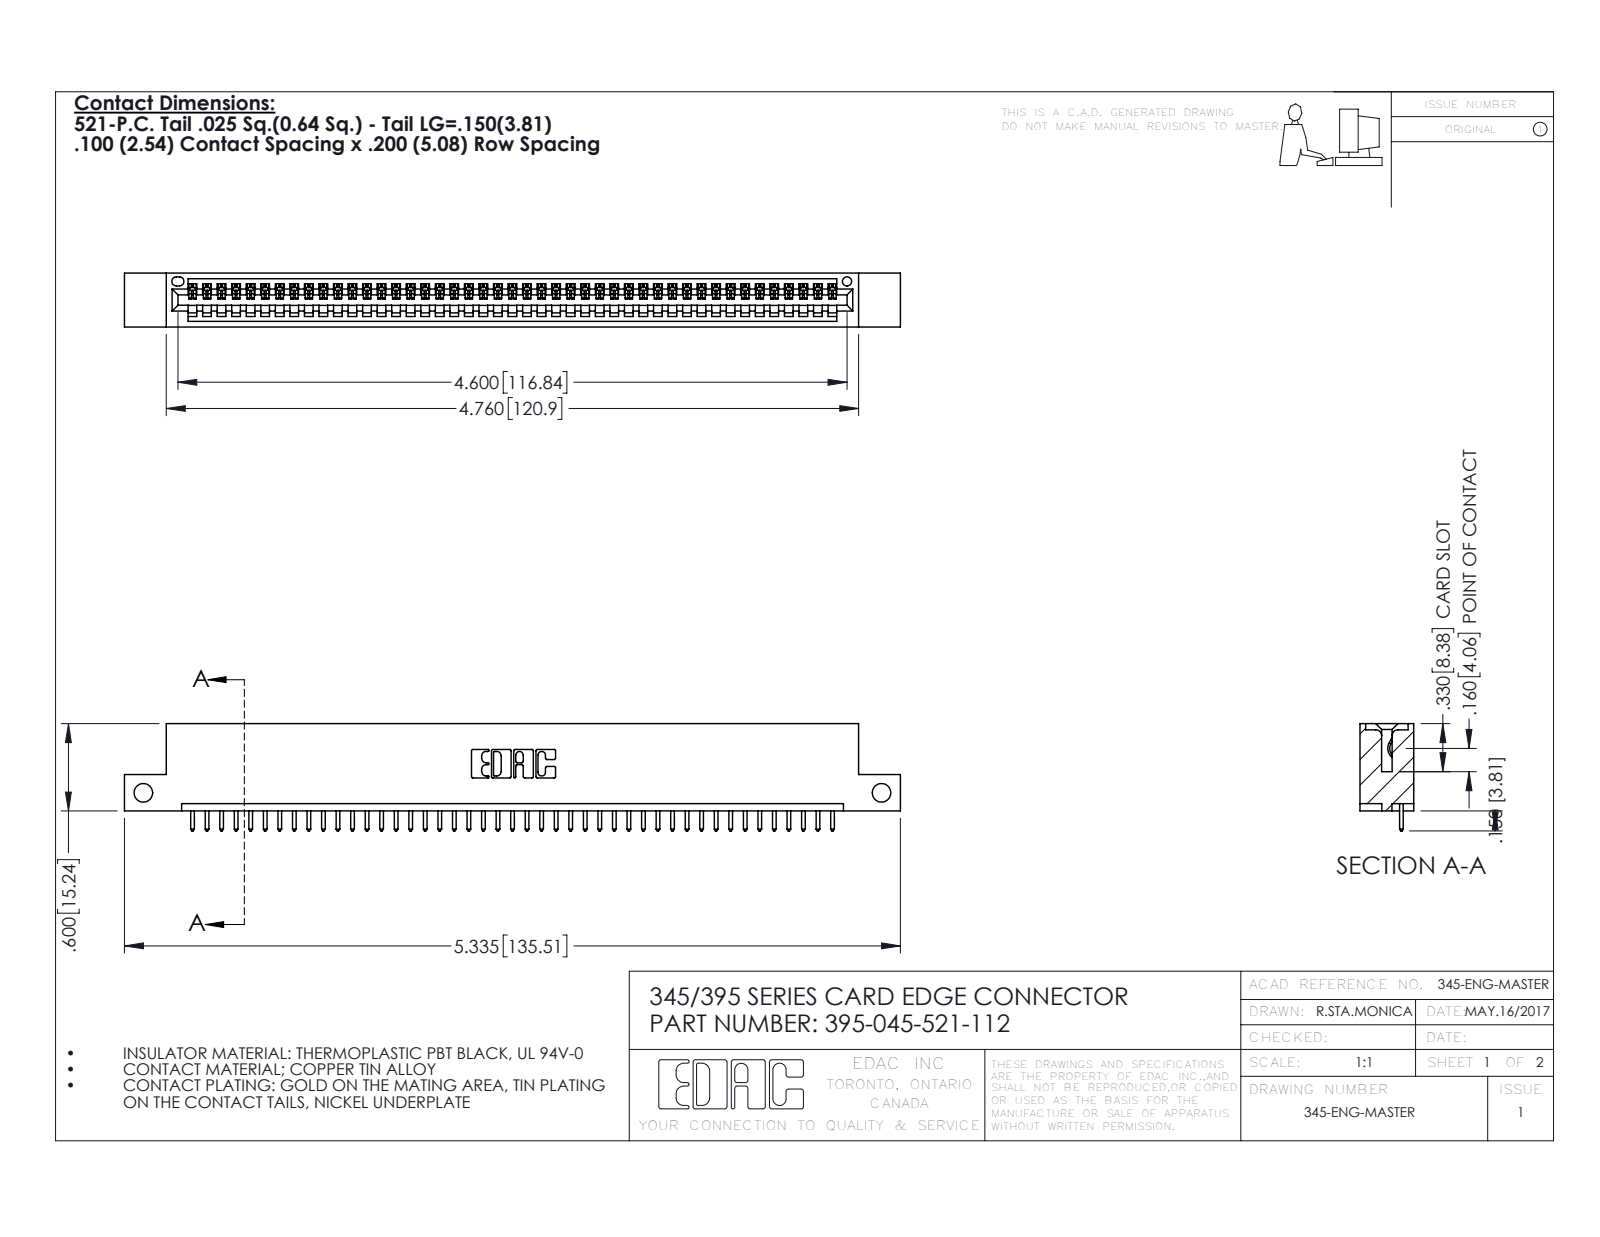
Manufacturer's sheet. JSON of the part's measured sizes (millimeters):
{"part_name": "345 Part_Flush Mounting Lugs - Side Mount; 345-292-001_345-293-121; 395-045-521-112", "step_written_by": "SolidWorks 2016 (CONFIG_CONTROL_DESIGN)", "units": "millimeters", "bodies": {"solids": 46, "faces": 2736, "planar": 1880, "cylindrical": 856, "other": 0}, "overall_size": [135.5, 18.7, 9.4], "volume_mm3": 12700, "surface_area_mm2": 16250, "round_holes": [[3.3, 2], [1.6, 1]], "partial_cylinders_radius": [[0.2, 90], [0.3, 90], [0.3, 22], [0.2, 6], [0.8, 6], [0.7, 3], [0.8, 2], [1, 2]], "face_to_face_distances": [7.6, 1.8, 9.4, 5.1, 2.5, 6.9, 0.6, 5.7, 3.8, 1.8], "hole_center_spacings": [128.9]}
